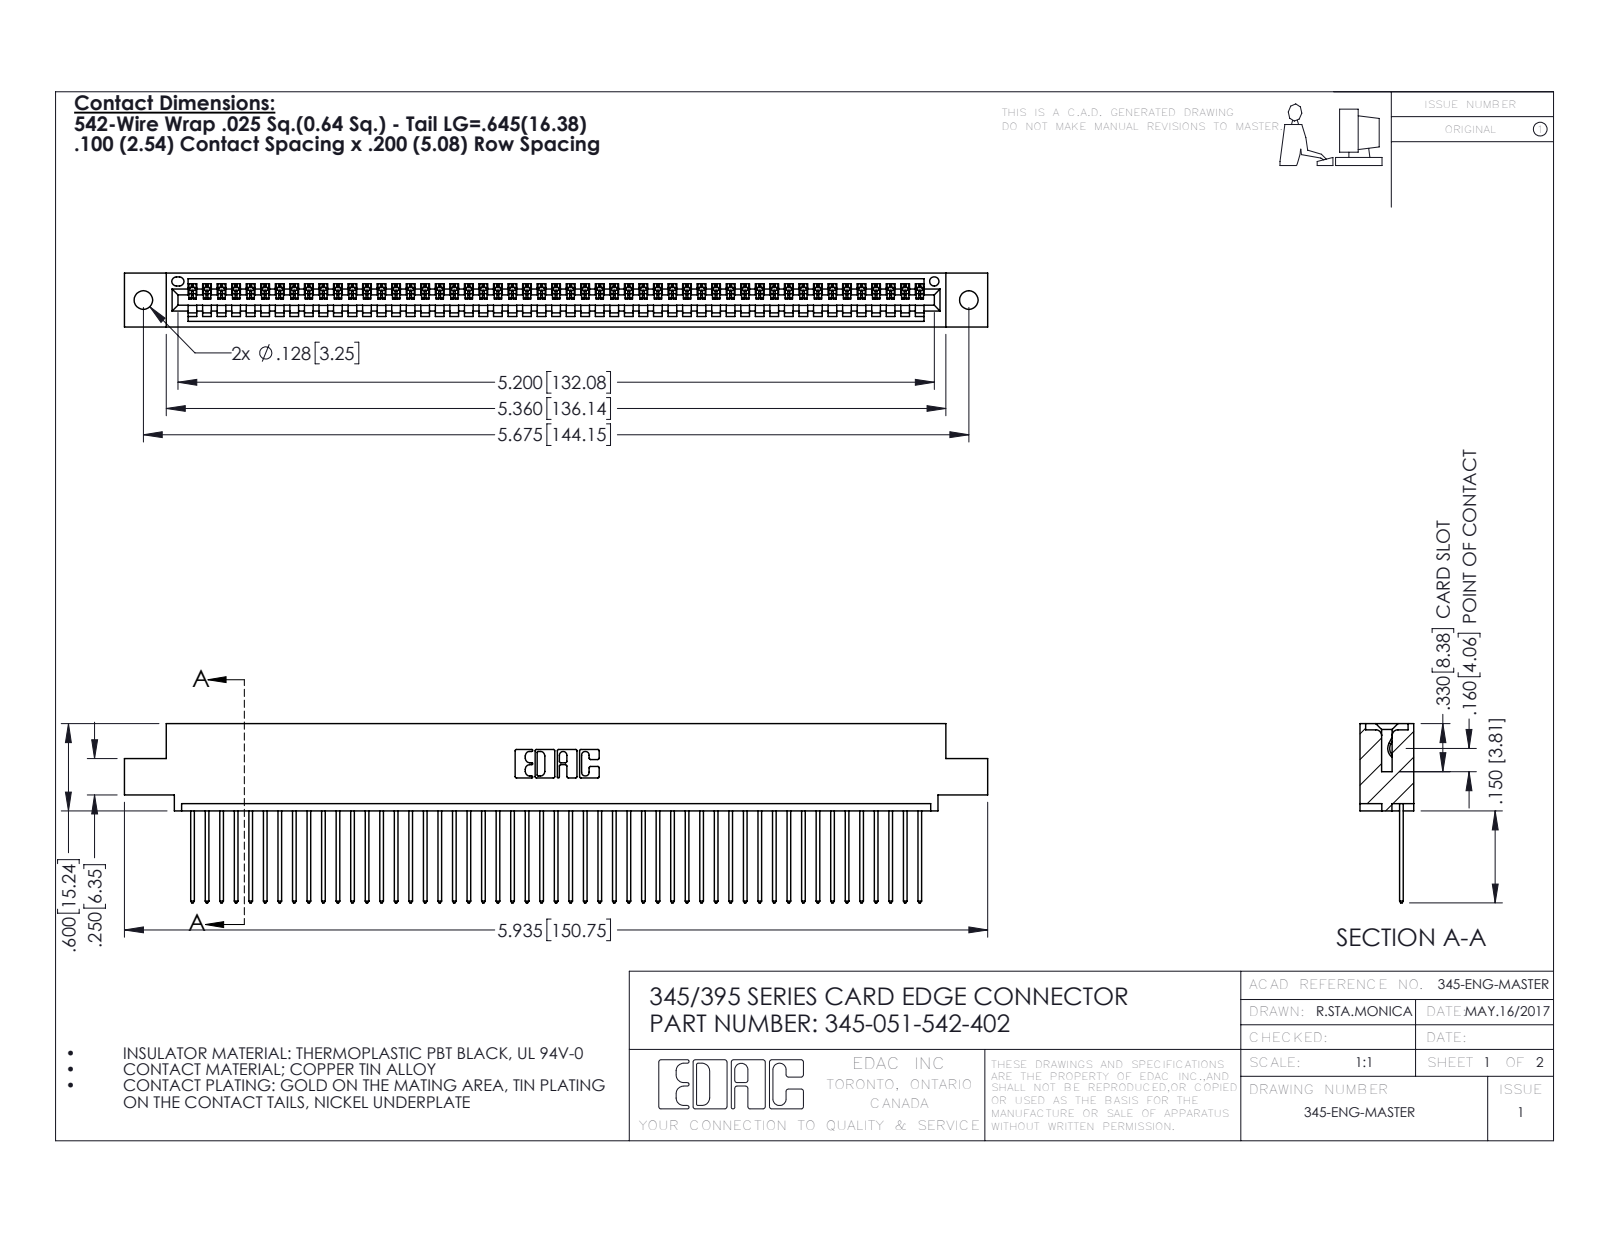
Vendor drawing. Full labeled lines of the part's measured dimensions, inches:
Part name (STEP PRODUCT): 345 Part_0.110 Offset - 0.128 Dia; 345-051-542-402; 345-292-001_345-293-142
STEP written by: SolidWorks 2016 (CONFIG_CONTROL_DESIGN)
Units: inches
Bodies: 52 solids, 3088 faces (2124 planar, 964 cylindrical, 0 other)
Overall size (bounding box): 5.935 × 1.232 × 0.37
Volume: 0.878 in³ · Surface area: 30.66 in²
Round holes (diameter × count): ⌀0.128 ×2, ⌀0.064 ×1
Partial cylindrical surfaces — rounded edges, fillets, slot ends (radius × count): R0.006 ×102, R0.01 ×102, R0.01 ×22, R0.007 ×6, R0.031 ×6, R0.026 ×3, R0.031 ×2, R0.04 ×2
Main face-to-face distances: 0.072, 0.298, 0.098, 0.272, 0.025, 0.37, 0.2, 0.225, 0.149, 0.072
Hole centre spacings: 0.27, 5.439, 5.675
